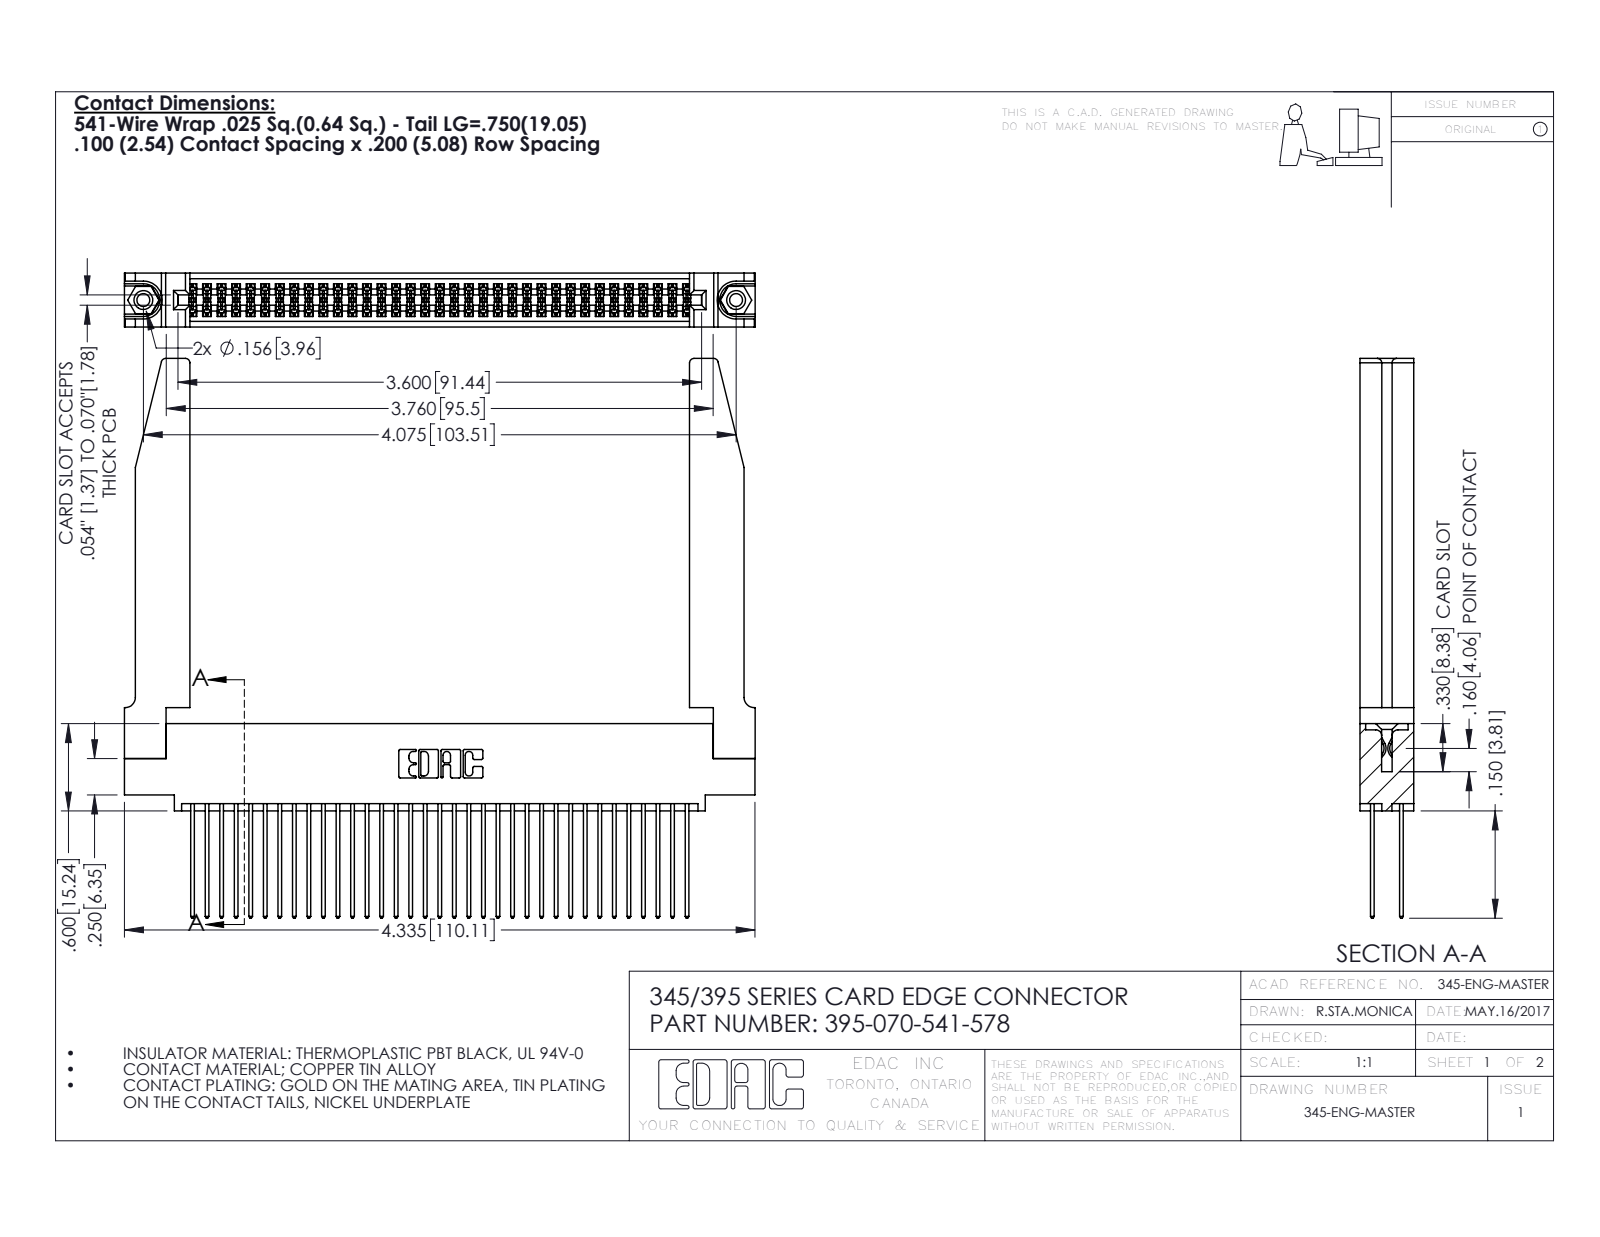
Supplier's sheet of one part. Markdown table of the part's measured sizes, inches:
| quantity | value |
| --- | --- |
| part name | 345 Part_0.110 Offset - 0.156 Dia-TH; 345-292-001_345-293-141; 345-250-001_345-250-001-102; 345-220-078_345-220-078 (+1 more) |
| STEP written by | SolidWorks 2016 (CONFIG_CONTROL_DESIGN) |
| units | inches |
| bodies | 75 solids, 3864 faces (2536 planar, 1276 cylindrical, 52 other) |
| overall size | 4.336 × 3.847 × 0.37 |
| volume | 1.143 in³ |
| surface area | 38.57 in² |
| round holes (diameter × count) | 0.089 × 2, 0.125 × 2, 0.156 × 2, 0.064 × 1 |
| round bosses / shafts (diameter × count) | 0.155 × 2 |
| partial cylindrical surfaces (radius × count) | 0.006 × 105, 0.01 × 70, 0.01 × 22, 0.03 × 8, 0.007 × 6, 0.031 × 6, 0.026 × 3, 0.014 × 2 |
| main face-to-face distances | 0.072, 0.298, 0.37, 0.098, 0.272, 0.025, 0.2, 0.225, 0.175, 0.148 |
| hole center spacings | 0.27, 3.839, 4.075 |
